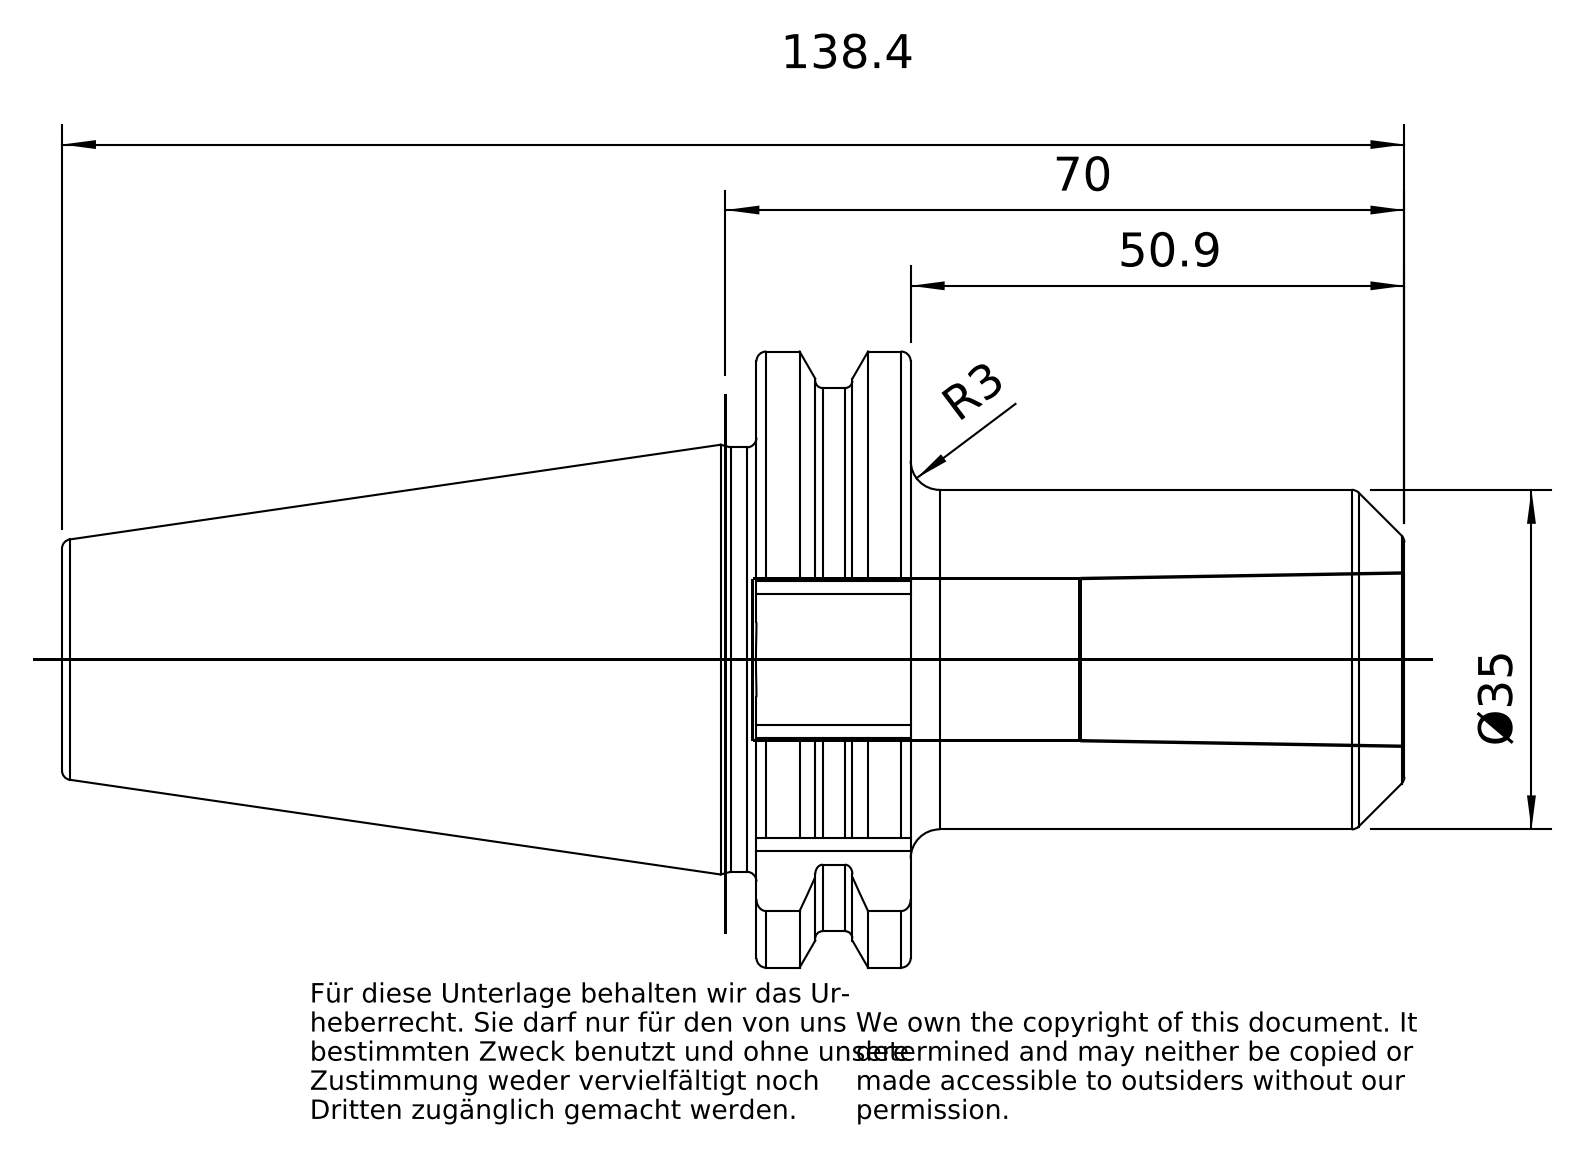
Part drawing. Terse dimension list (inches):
name: 40-420-02
written by: PRO/ENGINEER BY PARAMETRIC TECHNOLOGY CORPORATION, 2010430 (CONFIG_CONTROL_DESIGN)
unit: in
bodies: 1 solid, 101 faces (21 planar, 28 cylindrical, 52 other)
size: 5.443 × 2.501 × 2.418
volume: 8.45 in³; area: 44.32 in²
holes: 1× ⌀0.545, 1× ⌀0.658, 1× ⌀0.67, 1× ⌀0.689
bosses: 1× ⌀1.722, 1× ⌀1.378, 1× ⌀0.63
rounds: 5× R0.053, 1× R1.102, 1× R1.25
face distances: 0.624, 0.016, 0.64, 1.866, 2.646, 2.63, 2.006, 0.638, 2.797, 2.813
